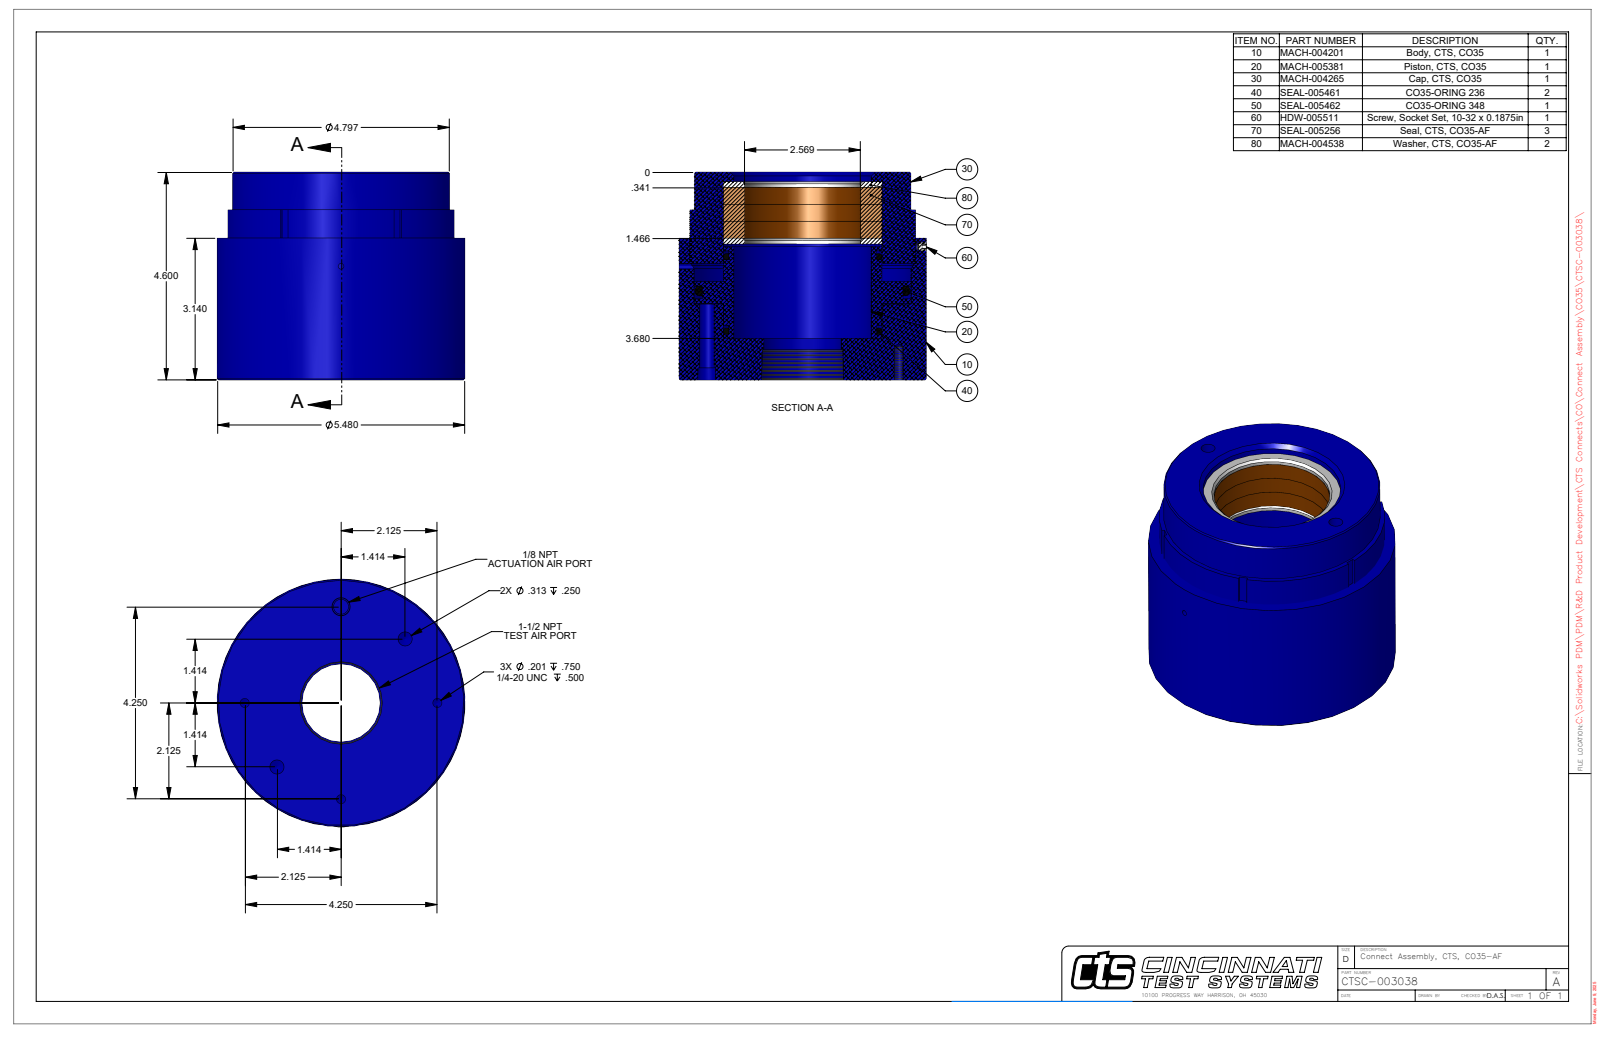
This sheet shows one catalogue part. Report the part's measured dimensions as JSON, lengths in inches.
{"part_name": "CTSC-003038", "step_written_by": "SolidWorks 2023 (AUTOMOTIVE_DESIGN)", "units": "inches", "bodies": {"solids": 2, "faces": 132, "planar": 50, "cylindrical": 58, "other": 24}, "overall_size": [5.486, 5.48, 4.6], "volume_in3": 74.81, "surface_area_in2": 181.6, "round_holes": [[0.313, 4], [0.201, 3], [0.125, 1], [0.332, 1], [1.719, 1], [2.569, 1], [2.571, 1], [3.05, 1], [3.08, 1], [3.517, 1]], "round_bosses_or_shafts": [[5.48, 1], [5, 1], [4.797, 1], [3.513, 1], [3.509, 1]], "partial_cylinders_radius": [[2.46, 1], [2.721, 1]], "face_to_face_distances": [4.6, 4.259, 0.341, 0.125, 4.384, 0.216, 0.92, 3.339, 3.464, 3.68], "hole_center_spacings": [1.583, 2, 2.125, 2.918, 3.005, 3.811, 0.125, 1.531]}
